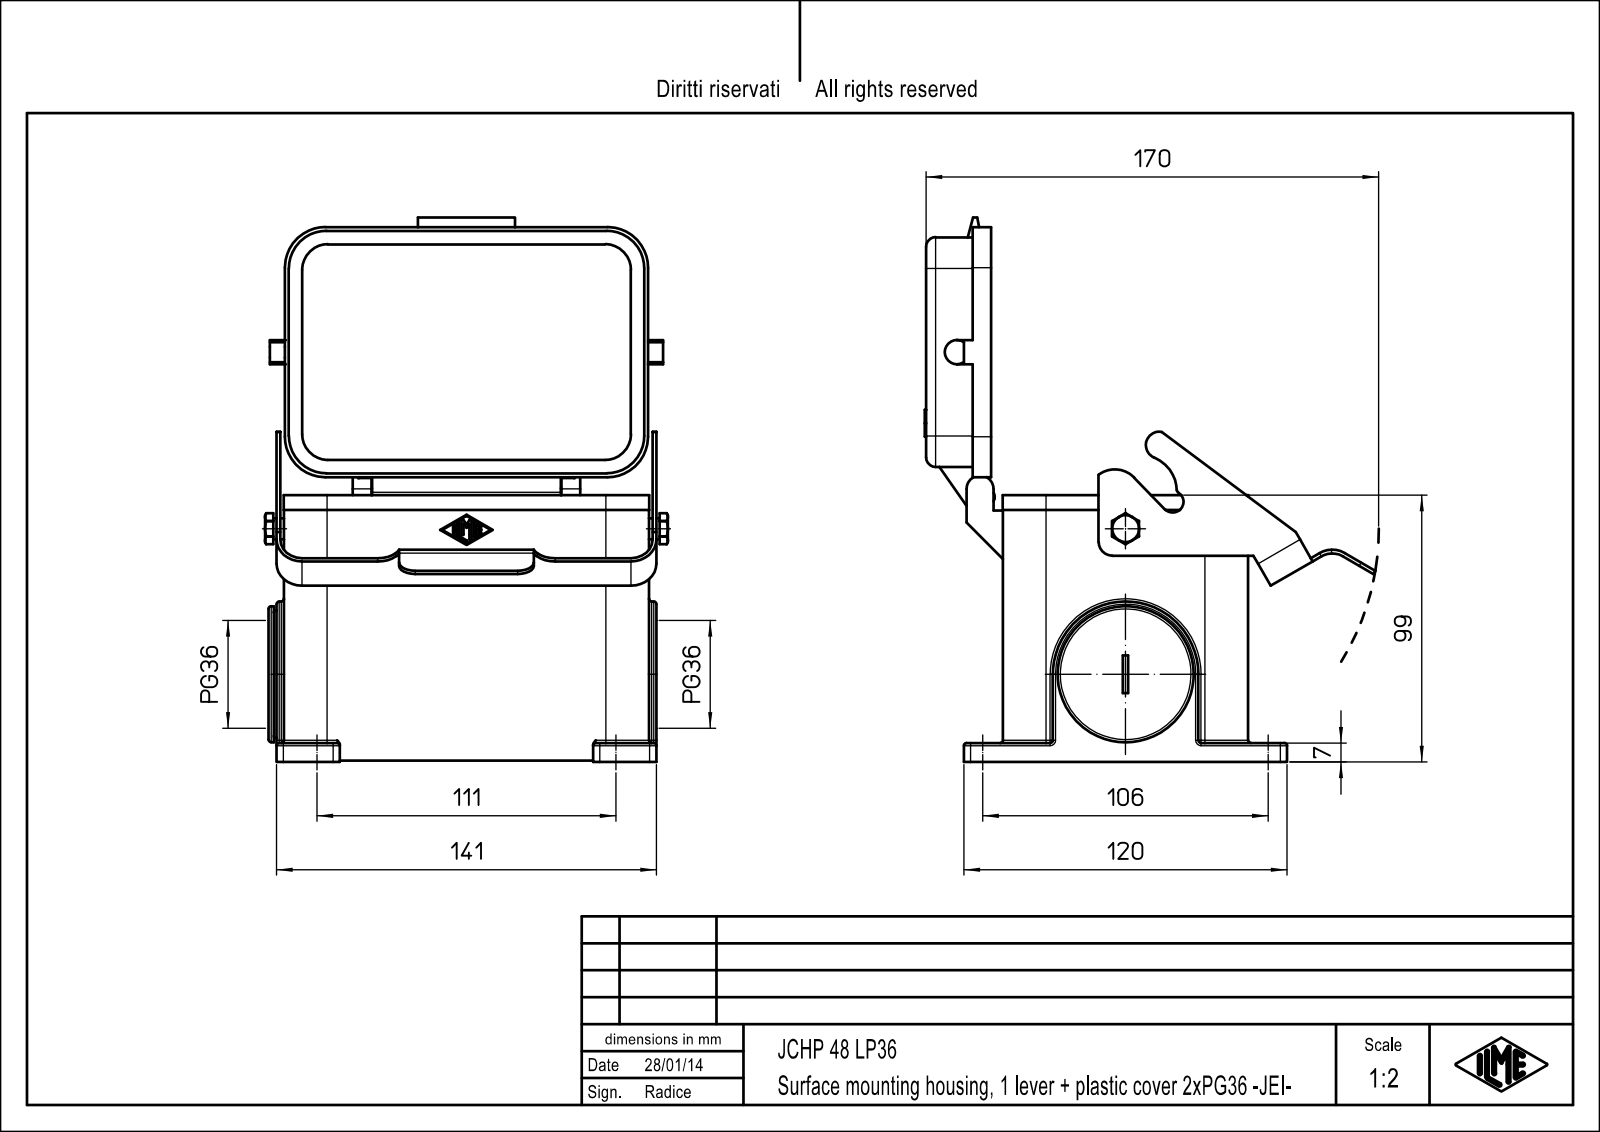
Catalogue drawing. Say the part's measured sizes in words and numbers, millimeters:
The part is named "JCHP_48_LP36". Its 3-D file was written by "Creo Elements/Direct Modeling 18.0B 02-Dec-2011 (C) Parametric Technology GmbH (AUTOMOTIVE_DESIGN)". It is 1 solid with 630 faces: 298 planar, 266 cylindrical and 66 other. Overall it measures 202.01 by 167.2 by 149.5 millimeters. Its volume is 438 104 cubic millimeters and its surface area 183 389 square millimeters. Round holes: 8 of diameter 2.46, 8 of diameter 3.1, 4 of diameter 6.5, 1 of diameter 5.5, 1 of diameter 38.48, 1 of diameter 42.48, 1 of diameter 45.48. Round bosses or shafts: 1 of diameter 50.48, 1 of diameter 7.8, 1 of diameter 6, 1 of diameter 5. Partial cylindrical surfaces (rounded edges, fillets, slot ends): 37 of radius 1, 15 of radius 0.33, 14 of radius 0.38, 9 of radius 3, 8 of radius 2.5, 5 of radius 8, 4 of radius 3.5, 4 of radius 9.5. The main face-to-face distances are 5, 86, 116.5, 111.5, 3, 119.5, 91, 25.5, 28.5, 81. The hole center spacings are 109.73, 22.28, 27, 35, 49.12, 57.11, 84.07, 104.
